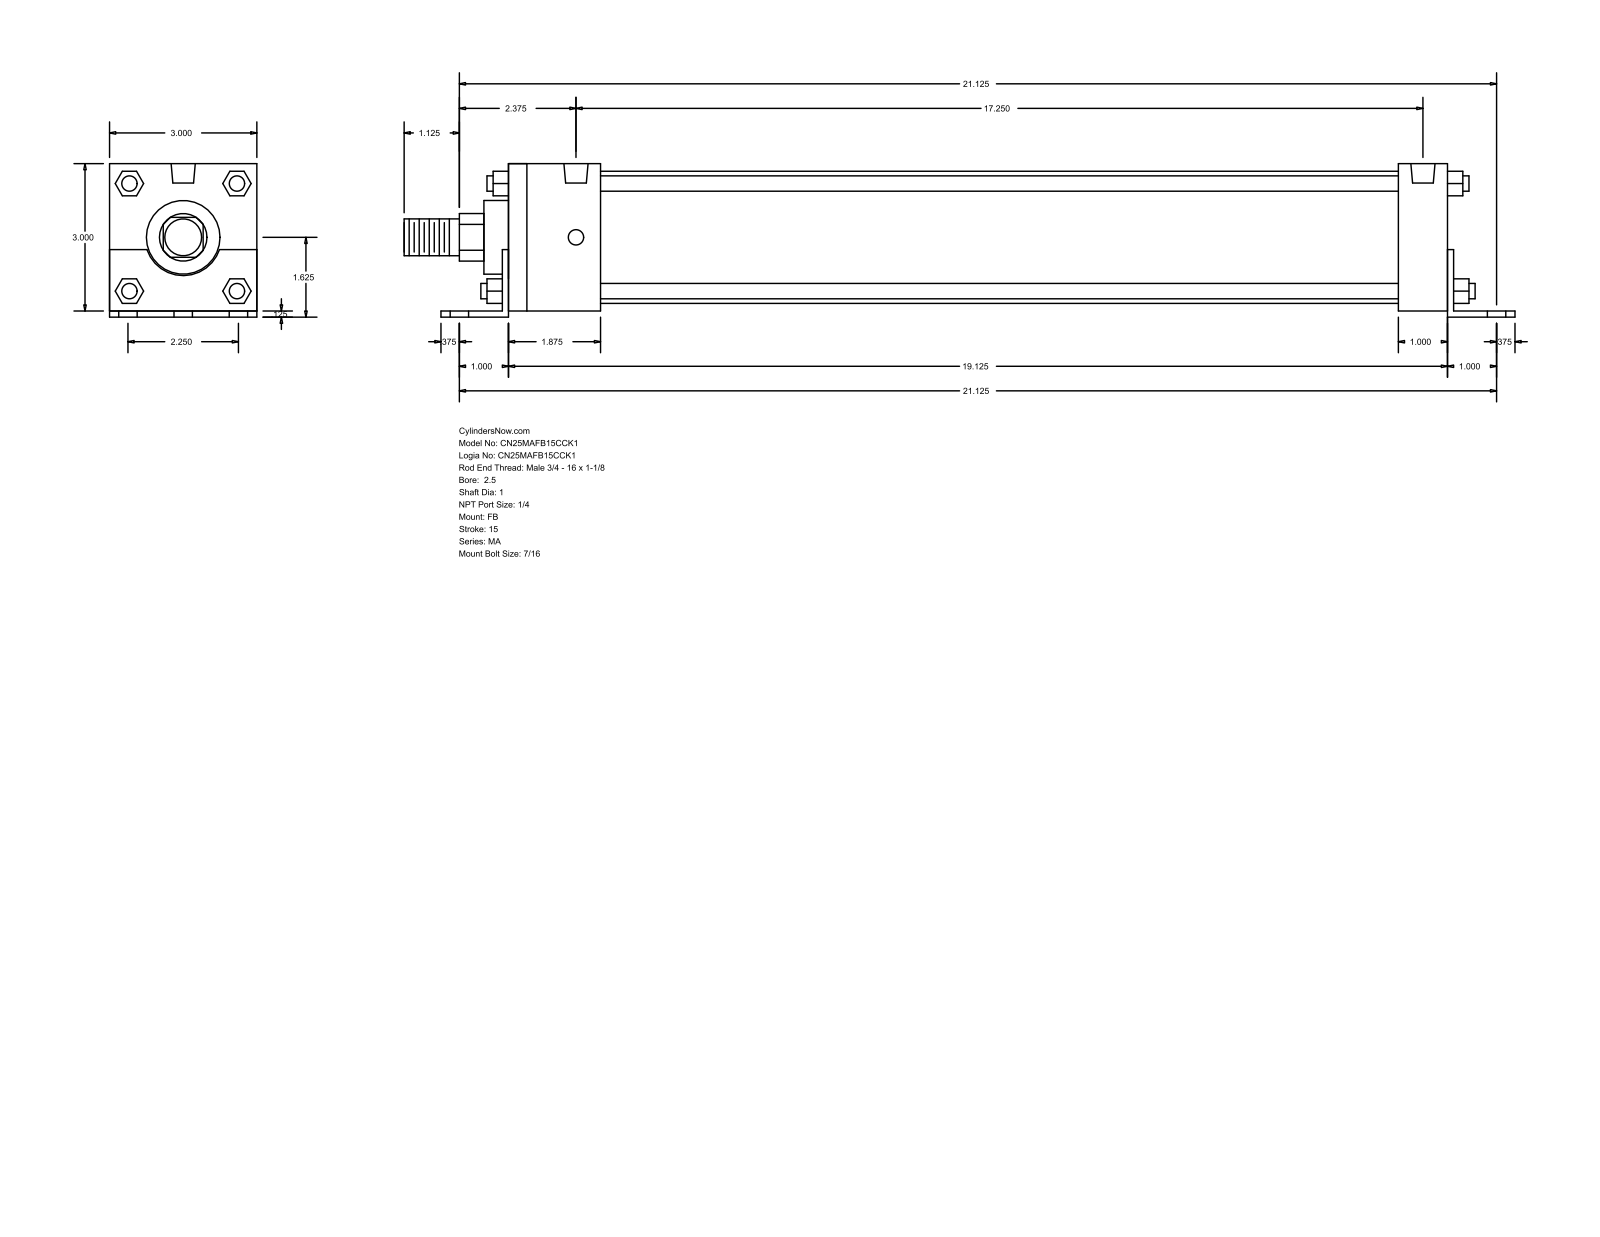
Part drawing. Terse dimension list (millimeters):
name: MA_FB__0250_1
written by: GSSL Pune (CONFIG_CONTROL_DESIGN)
unit: mm
bodies: 0 solids, 140 faces (105 planar, 35 cylindrical, 0 other)
size: 574.67 × 79.38 × 76.2
holes: 6× ⌀11.11, 4× ⌀7.94, 2× ⌀12.49
bosses: 4× ⌀7.94, 1× ⌀68.33, 1× ⌀38.1, 1× ⌀25.4, 1× ⌀19.05
rounds: 1× R12.29, 1× R19.81
face distances: 76.2, 3.17, 79.37, 488.95, 485.78, 12.7, 50.8, 47.63, 438.15, 441.32
hole spacings: 28.57, 537.34, 536.58, 47.62, 57.14, 66.75, 438.15, 477.11
